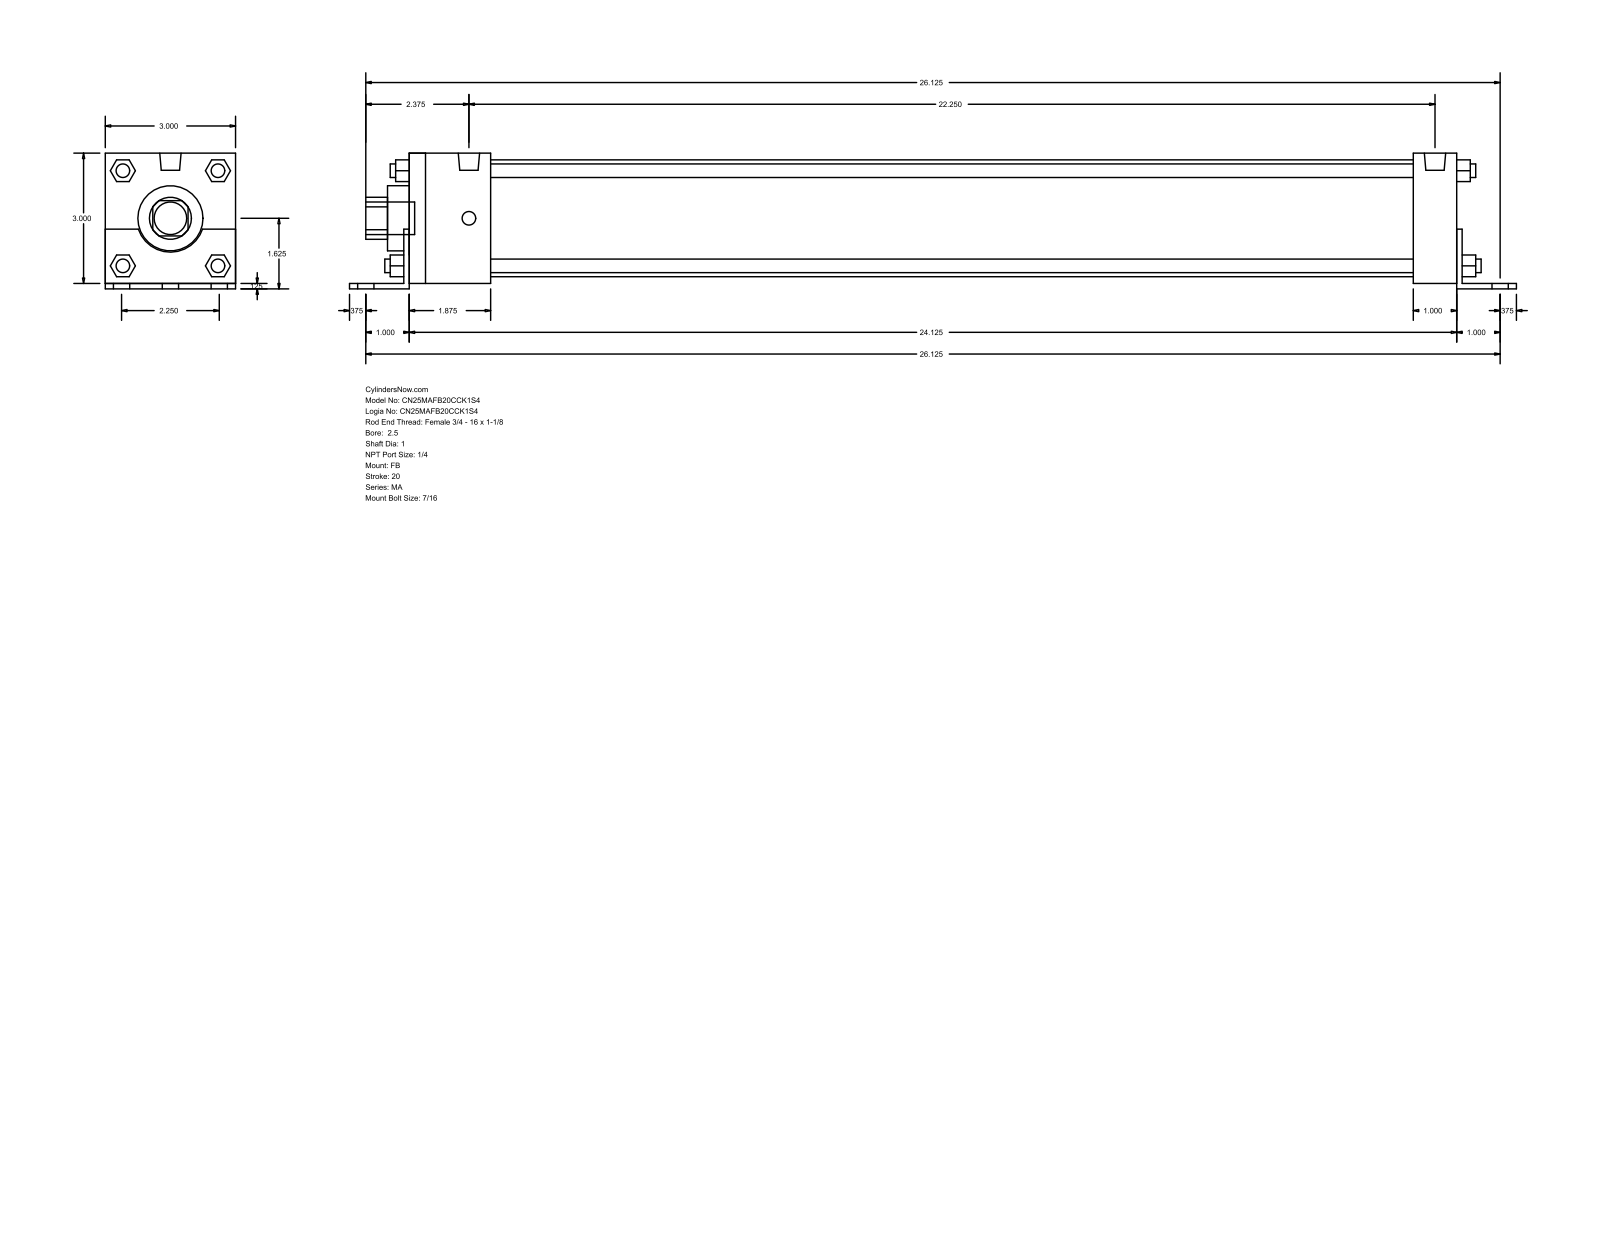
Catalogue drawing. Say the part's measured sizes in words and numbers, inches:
The part is named "MA_FB__0250_1". Its 3-D file was written by "GSSL Pune (CONFIG_CONTROL_DESIGN)". It is 0 solids with 140 faces: 105 planar, 35 cylindrical and 0 other. Overall it measures 26.875 by 3.125 by 3 inches. Round holes: 1 of diameter 1, 1 of diameter 1.5, 1 of diameter 2.69. Round bosses or shafts: 8 of diameter 0.313, 6 of diameter 0.437, 2 of diameter 0.492, 1 of diameter 0.75. Partial cylindrical surfaces (rounded edges, fillets, slot ends): 1 of radius 0.484, 1 of radius 0.78. The main face-to-face distances are 3, 0.125, 3.125, 24.125, 0.125, 0.5, 24.25, 1, 1.875, 22.25.
